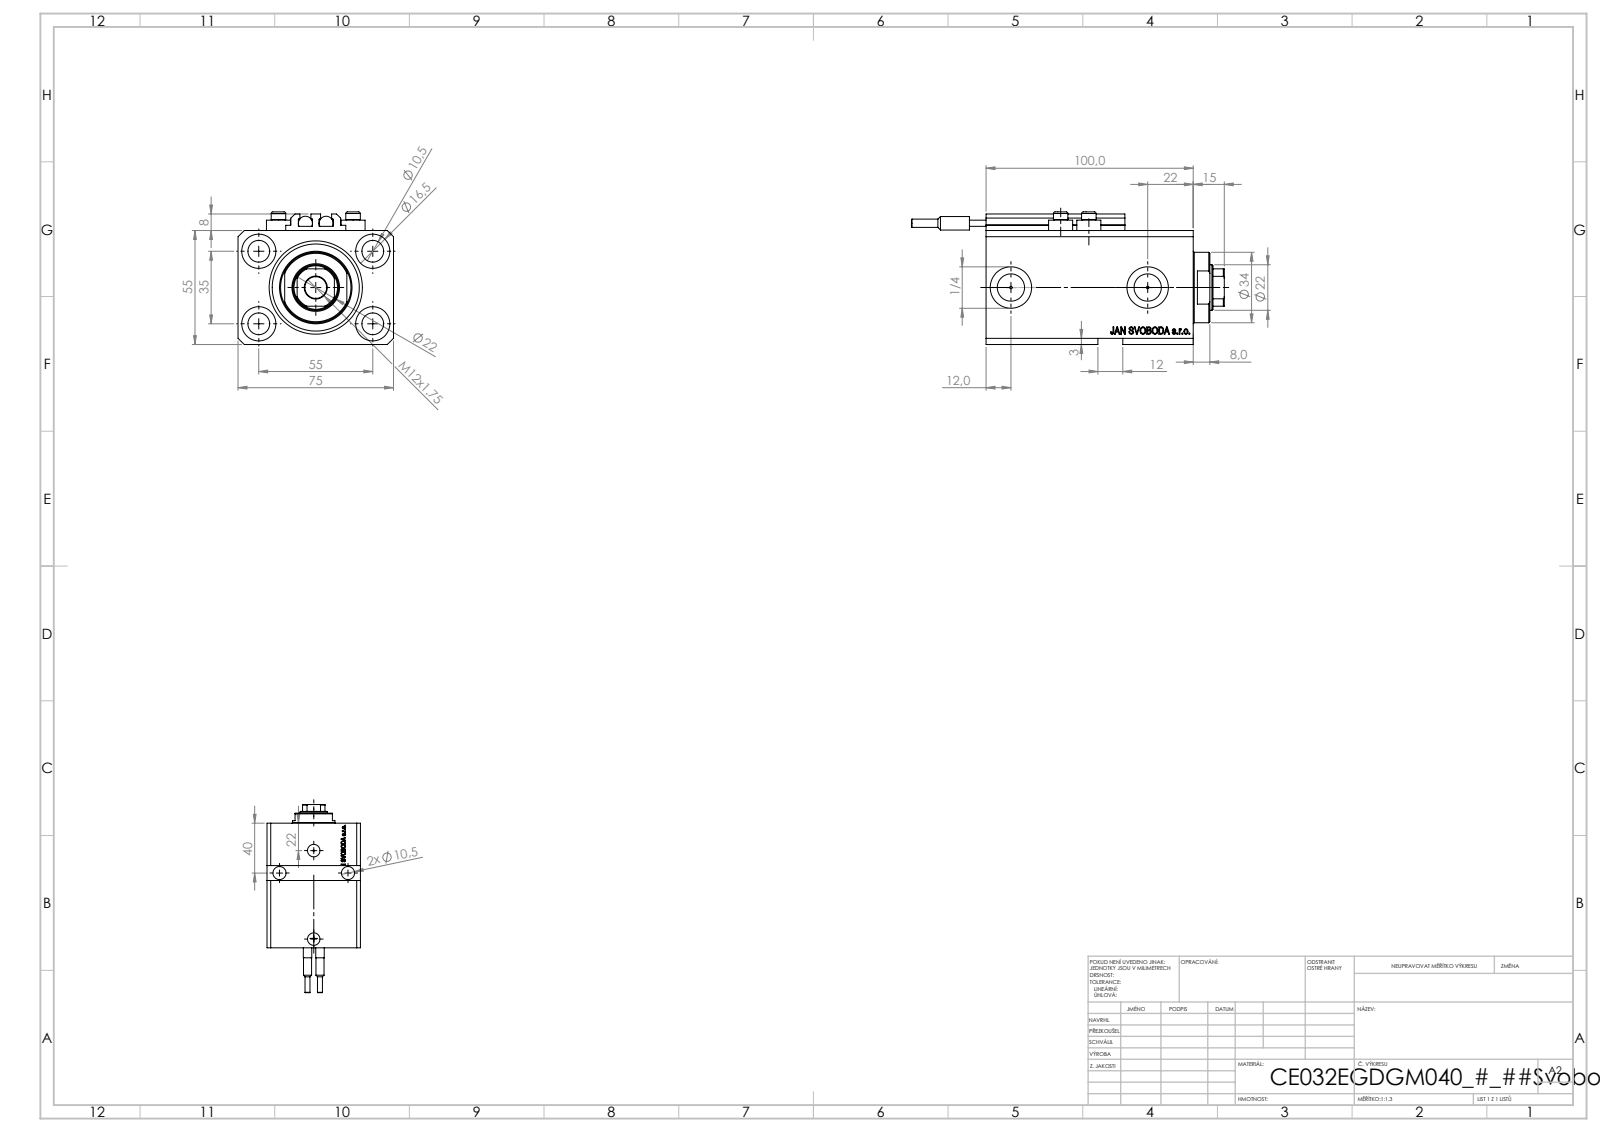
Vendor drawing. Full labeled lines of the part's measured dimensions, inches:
Part name (STEP PRODUCT): V250CE_C_VCP; SWITCH_V250CE; V250CE_E_Body; V250CE_VC_E (+1 more)
STEP written by: SolidWorks 2019 (CONFIG_CONTROL_DESIGN)
Units: inches
Bodies: 10 solids, 1132 faces (550 planar, 150 cylindrical, 432 other)
Overall size (bounding box): 5.945 × 2.953 × 2.52
Volume: 21.55 in³ · Surface area: 141.8 in²
Round holes (diameter × count): ⌀0.413 ×7, ⌀0.049 ×4, ⌀0.157 ×4, ⌀0.65 ×4, ⌀0.394 ×2, ⌀0.518 ×2, ⌀0.787 ×2, ⌀0.866 ×1, ⌀1.26 ×1, ⌀1.772 ×1
Round bosses / shafts (diameter × count): ⌀0.457 ×4, ⌀0.276 ×4, ⌀0.268 ×2, ⌀0.256 ×2, ⌀0.157 ×2, ⌀1.339 ×1
Partial cylindrical surfaces — rounded edges, fillets, slot ends (radius × count): R0.008 ×10, R0.413 ×1
Main face-to-face distances: 2.165, 2.953, 0.118, 0.591, 3.937, 3.346, 2.244, 0.39, 2.957, 3.547
Hole centre spacings: 1.283, 2.165, 0.535, 0.555, 1.016, 1.294, 1.324, 1.326
